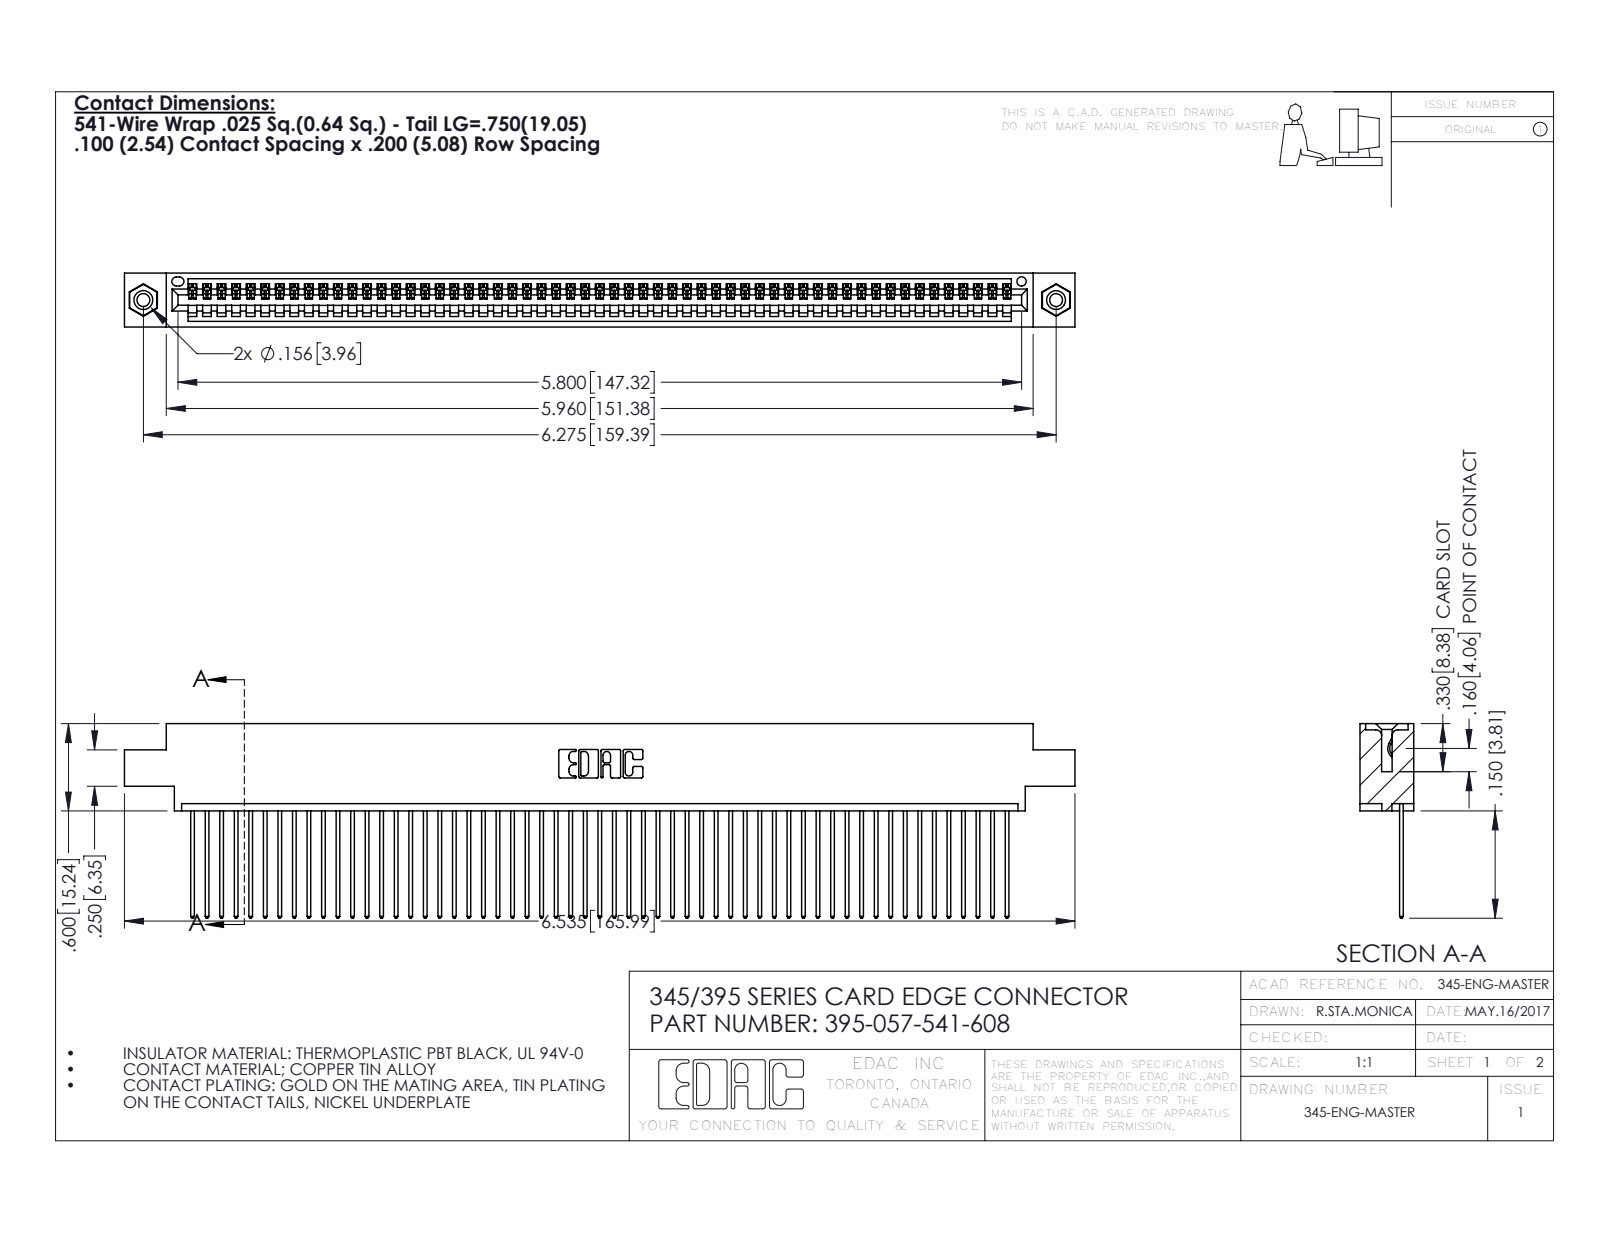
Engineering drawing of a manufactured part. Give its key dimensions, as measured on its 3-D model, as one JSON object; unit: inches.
{"part_name": "345-250-001_345-250-003-102; 345 Part_0.170 Offset - 0.156 Dia-TI; 345-292-001_345-293-141; 395-057-541-608", "step_written_by": "SolidWorks 2016 (CONFIG_CONTROL_DESIGN)", "units": "inches", "bodies": {"solids": 60, "faces": 3496, "planar": 2396, "cylindrical": 1084, "other": 16}, "overall_size": [6.535, 1.337, 0.37], "volume_in3": 0.974, "surface_area_in2": 35.13, "round_holes": [[0.089, 2], [0.125, 2], [0.156, 2], [0.064, 1]], "round_bosses_or_shafts": [[0.155, 2]], "partial_cylinders_radius": [[0.006, 114], [0.01, 114], [0.01, 22], [0.007, 6], [0.031, 6], [0.026, 3], [0.031, 2], [0.04, 2]], "face_to_face_distances": [0.072, 0.298, 0.098, 0.272, 0.025, 0.37, 0.2, 0.225, 0.175, 0.149], "hole_center_spacings": [0.27, 6.039, 6.275]}
